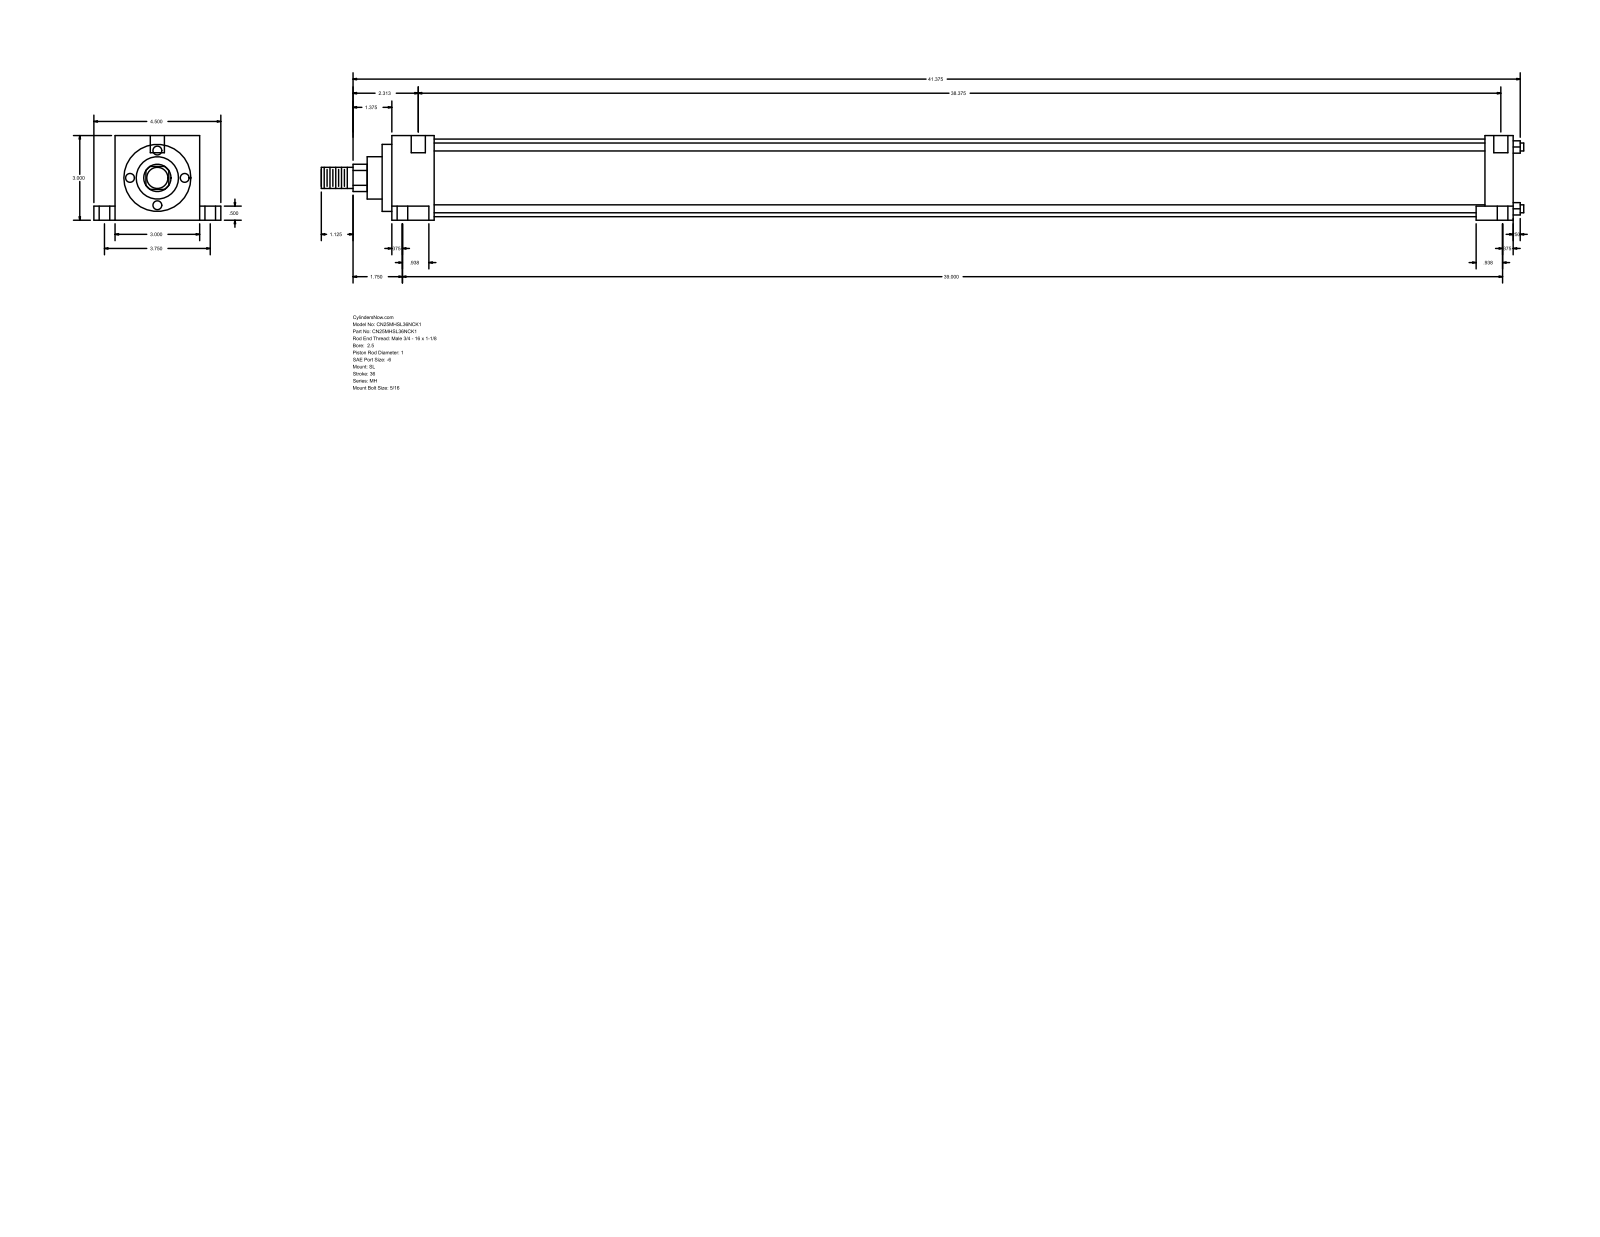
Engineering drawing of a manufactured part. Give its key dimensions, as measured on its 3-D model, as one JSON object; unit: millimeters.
{"part_name": "MH_SL__0250_1", "step_written_by": "GSSL Pune (CONFIG_CONTROL_DESIGN)", "units": "millimeters", "bodies": {"solids": 0, "faces": 86, "planar": 61, "cylindrical": 25, "other": 0}, "overall_size": [1082.67, 114.3, 76.2], "round_holes": [[5.56, 2], [9.53, 2], [15.88, 2], [12.7, 1]], "round_bosses_or_shafts": [[7.14, 4], [69.85, 1], [60.33, 1], [38.1, 1], [25.4, 1], [19.05, 1]], "partial_cylinders_radius": [[12.29, 1]], "face_to_face_distances": [76.2, 25.41, 992.98, 1018.39, 12.7, 63.5, 19.05, 95.25, 13.49, 1006.47], "hole_center_spacings": [47.65, 3.18, 95.24]}
